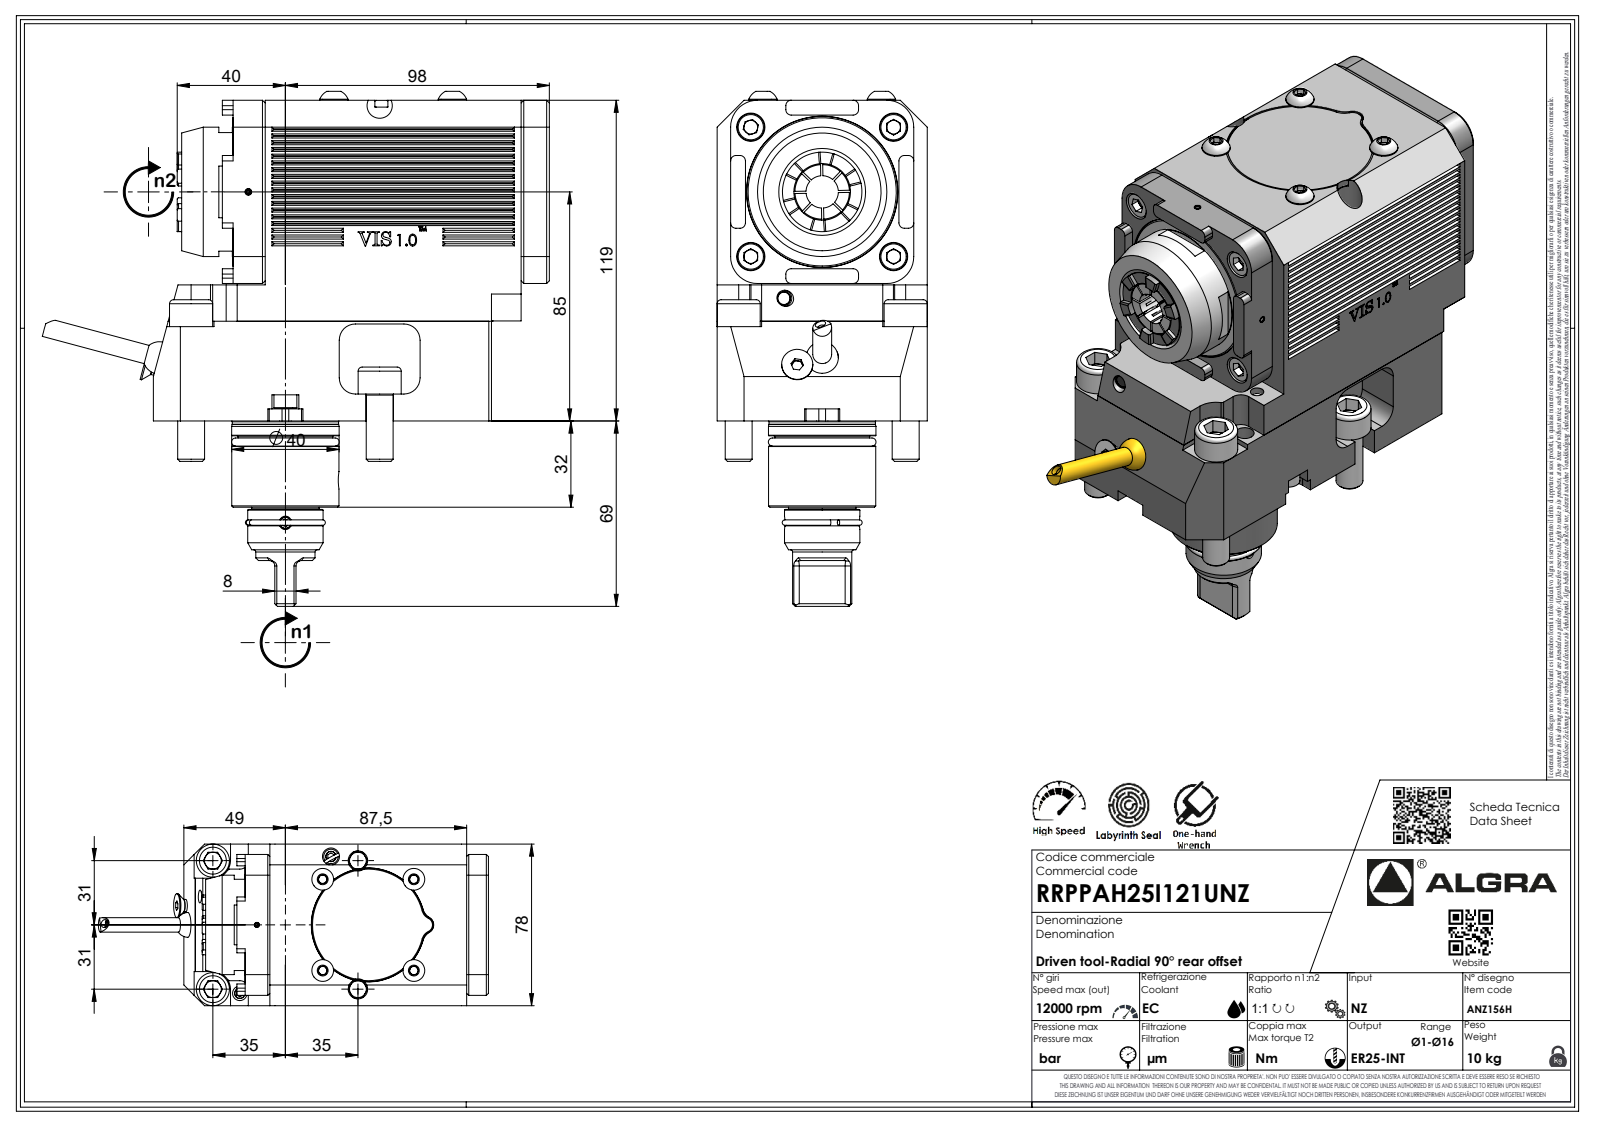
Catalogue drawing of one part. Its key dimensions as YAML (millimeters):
part_name: "RRPPAH25I121UNZ"
step_written_by: "SolidWorks 2023 (AUTOMOTIVE_DESIGN)"
units: millimeters
bodies: {solids: 1, faces: 506, planar: 333, cylindrical: 81, other: 92}
overall_size: [187.8, 147.5, 78]
volume: 1178000
surface_area: 82639
round_holes:
  - {diameter: 2.1, count: 1}
round_bosses_or_shafts:
  - {diameter: 10, count: 4}
  - {diameter: 16, count: 2}
  - {diameter: 48, count: 1}
  - {diameter: 39.9, count: 1}
  - {diameter: 39.8, count: 1}
  - {diameter: 39.5, count: 1}
  - {diameter: 35.1, count: 1}
  - {diameter: 28, count: 1}
partial_cylinders:
  - {radius: 2, count: 22}
  - {radius: 0.33, count: 7}
  - {radius: 0.52, count: 7}
  - {radius: 3.7, count: 7}
  - {radius: 10, count: 4}
  - {radius: 1, count: 2}
  - {radius: 4.1, count: 2}
  - {radius: 8.5, count: 2}
face_to_face_distances: [78, 119, 11, 22, 50.5, 5, 73, 68.5, 68, 95.9]
